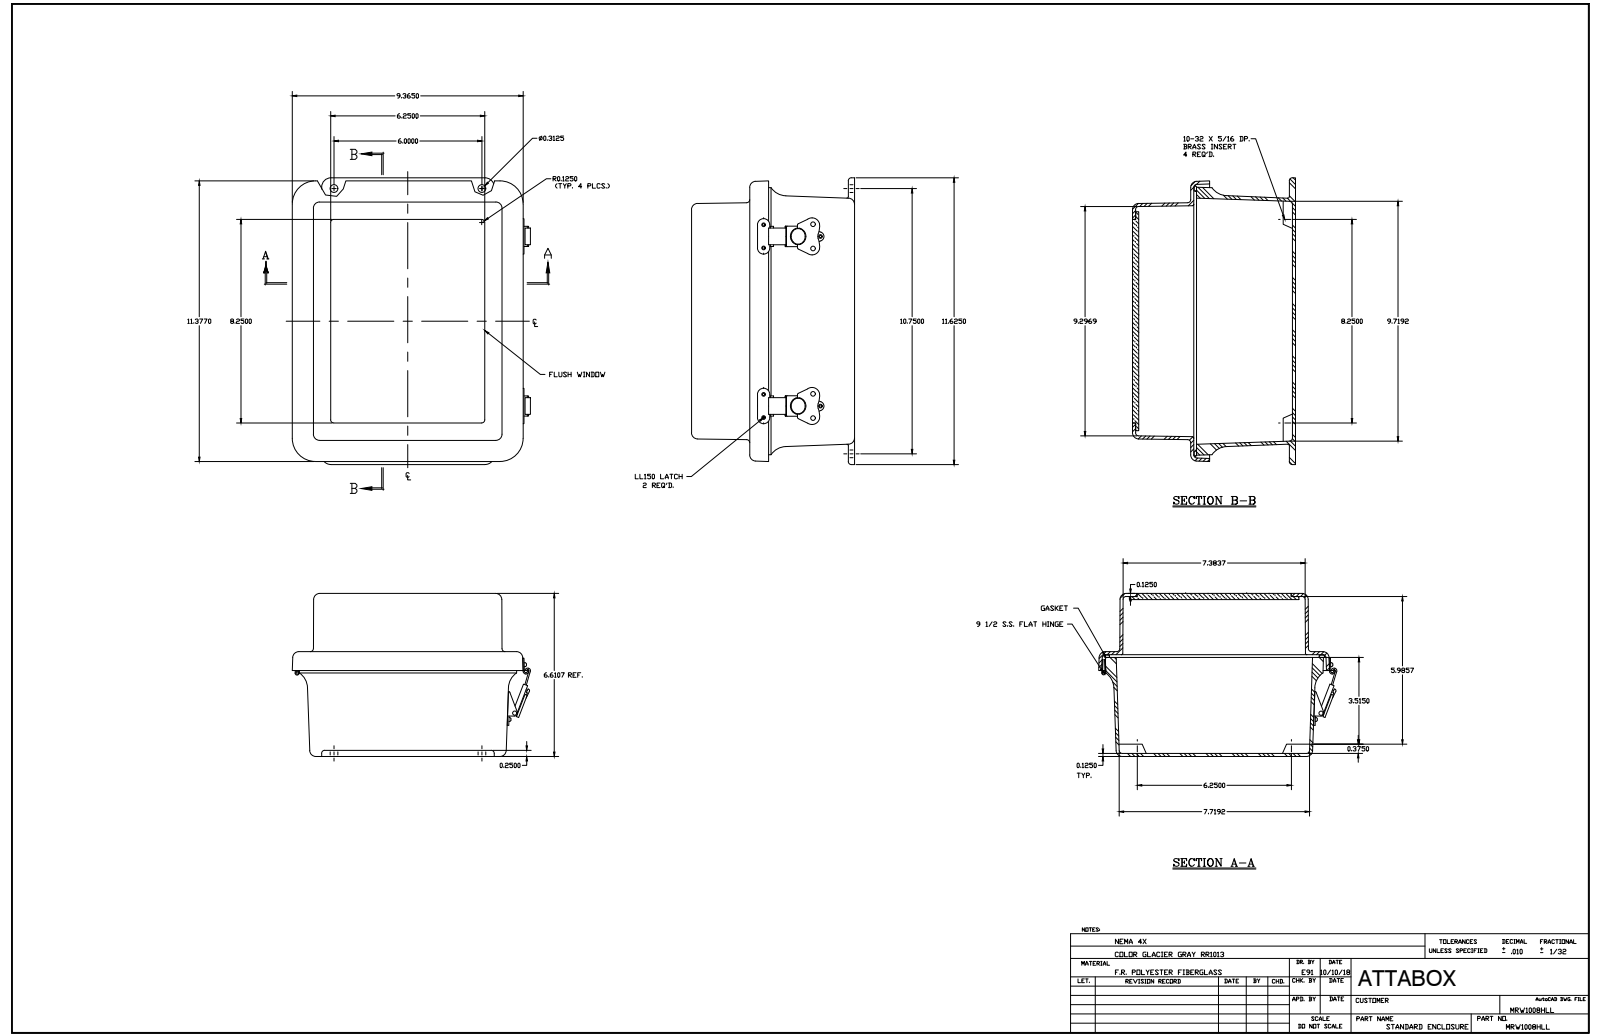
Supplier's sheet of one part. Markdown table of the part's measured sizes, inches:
| quantity | value |
| --- | --- |
| part name | MRW1008HLL |
| STEP written by | SolidWorks 2018 (AUTOMOTIVE_DESIGN) |
| units | inches |
| bodies | 49 solids, 1178 faces (510 planar, 453 cylindrical, 215 other) |
| overall size | 11.625 × 9.592 × 6.579 |
| volume | 76.66 in³ |
| surface area | 1 014 in² |
| round holes (diameter × count) | 0.14 × 16, 0.131 × 8, 0.156 × 6, 0.152 × 5, 0.13 × 4, 0.165 × 4, 0.197 × 4, 0.218 × 4, 0.118 × 2, 0.138 × 2, 0.181 × 2, 0.182 × 2 |
| round bosses / shafts (diameter × count) | 0.25 × 16, 0.125 × 11, 0.125 × 5, 0.27 × 4, 0.583 × 2, 0.524 × 2, 0.209 × 2, 0.185 × 2 |
| partial cylindrical surfaces (radius × count) | 0.125 × 28, 0.031 × 20, 0.079 × 19, 0.25 × 16, 0.037 × 8, 0.039 × 8, 0.045 × 8, 0.047 × 8 |
| main face-to-face distances | 0.125, 6.329, 0.25, 6.579, 6.454, 6.204, 4.094, 2.235, 0.125, 3.969 |
| hole center spacings | 7, 6, 3, 7.251, 6.25, 0.118, 0.25, 0.616 |
